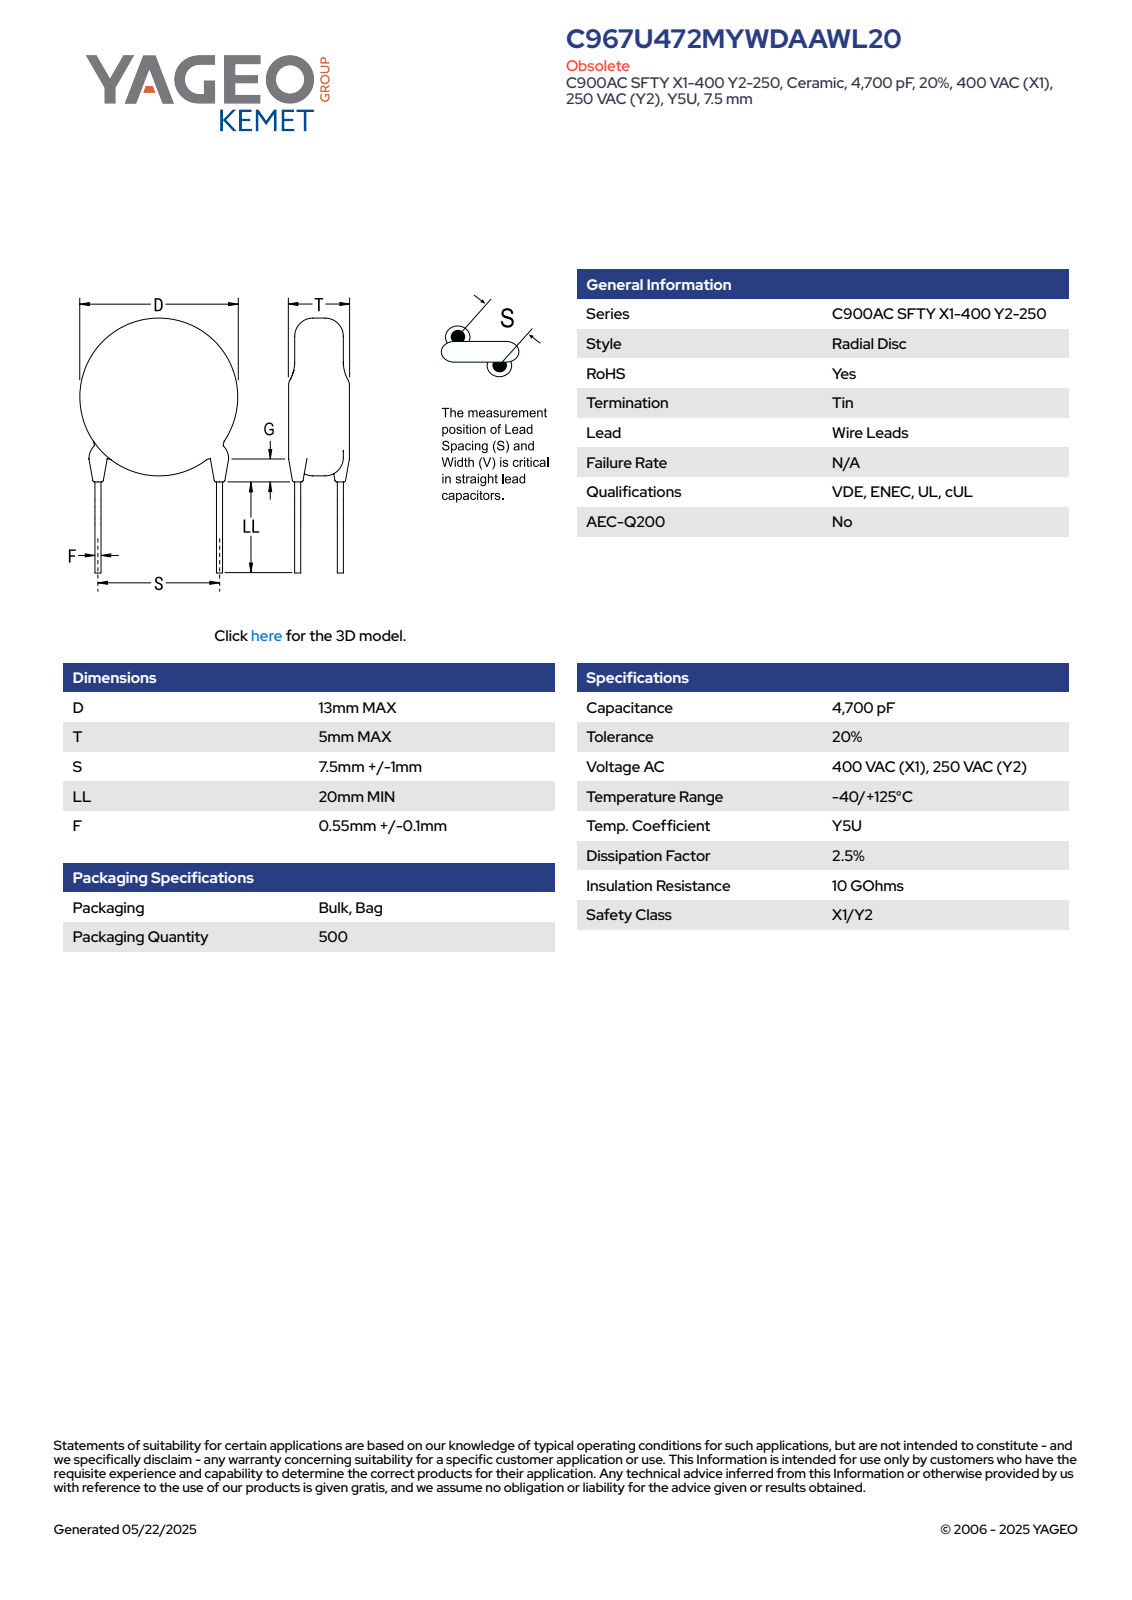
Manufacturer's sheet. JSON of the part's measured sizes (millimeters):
{"part_name": "CCD_STC900_D13T5S7.5LL20F0.65G3", "step_written_by": "SolidWorks 2014 (AUTOMOTIVE_DESIGN)", "units": "millimeters", "bodies": {"solids": 4, "faces": 83, "planar": 61, "cylindrical": 6, "other": 16}, "overall_size": [33.23, 13, 5], "volume_mm3": 662, "surface_area_mm2": 535, "round_bosses_or_shafts": [[0.65, 2], [13, 1]], "face_to_face_distances": [5, 1.5, 27.48, 25.98, 0.41, 6.13, 0.93, 3.1, 4.45, 4.63]}
